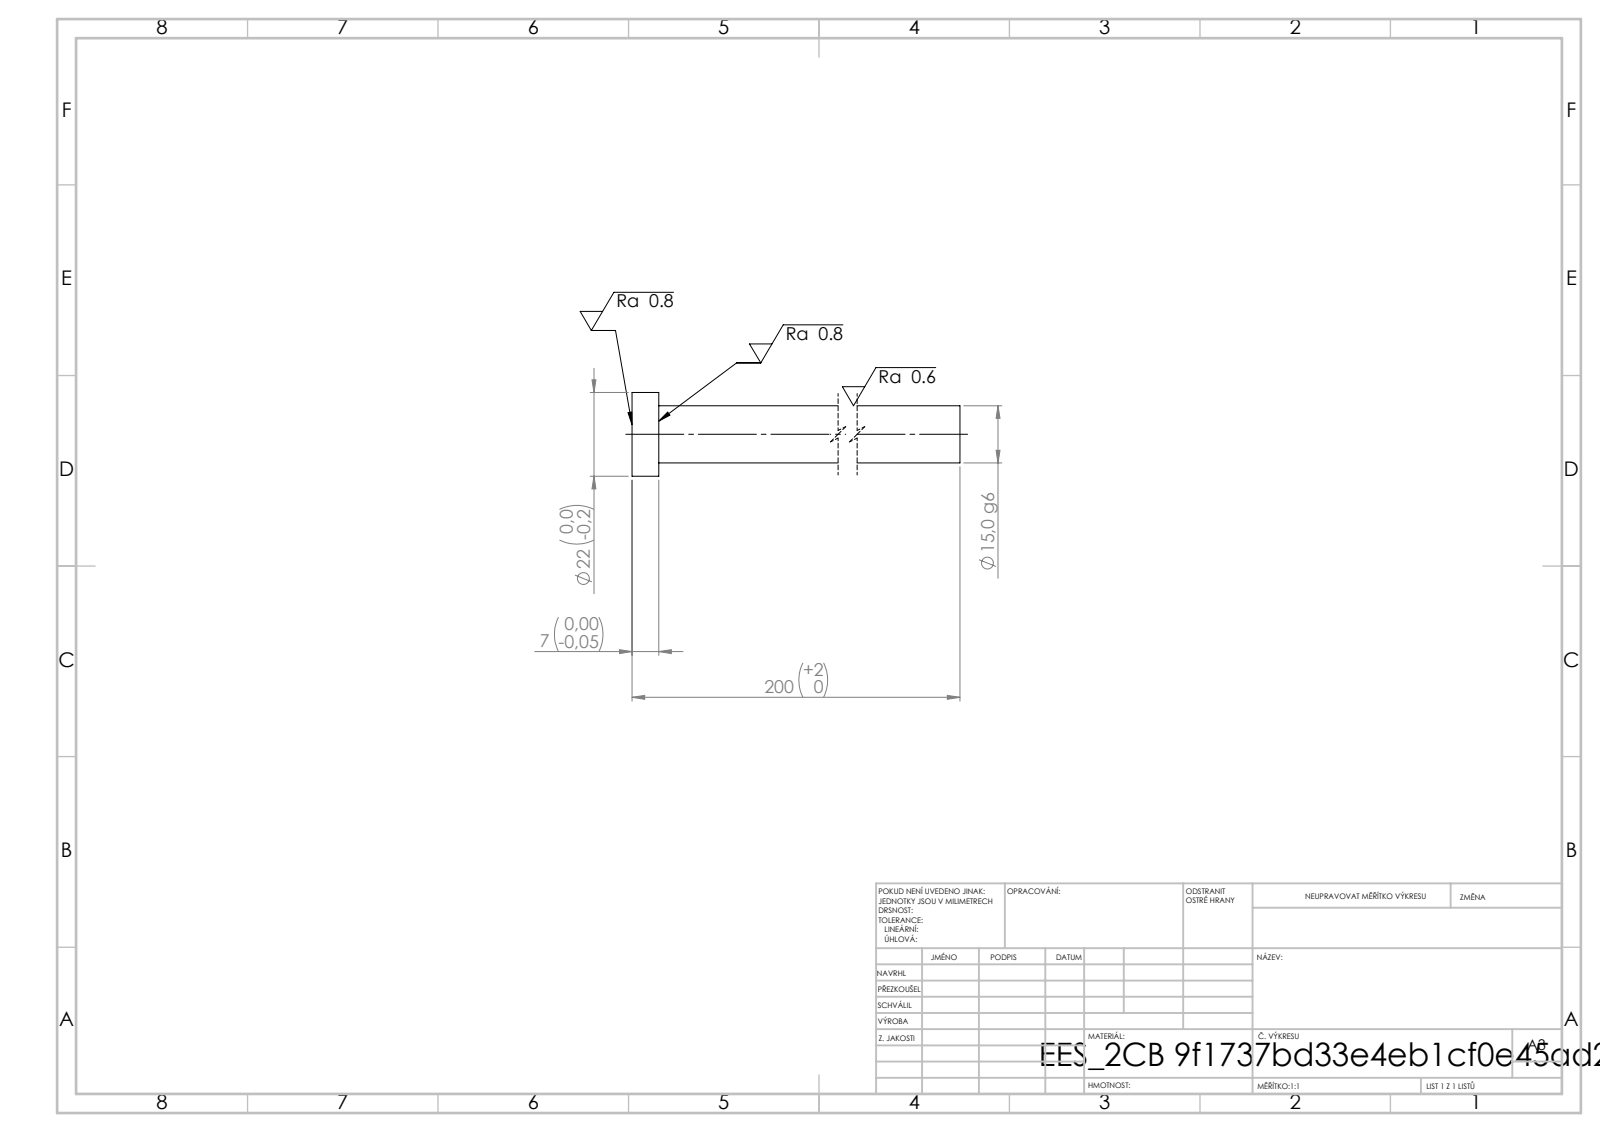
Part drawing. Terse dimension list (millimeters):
written by: SolidWorks 2019 (CONFIG_CONTROL_DESIGN)
unit: mm
bodies: 1 solid, 7 faces (3 planar, 4 cylindrical, 0 other)
size: 200 × 22 × 22
volume: 36 767 mm³; area: 10 339 mm²
bosses: 1× ⌀22, 1× ⌀15
face distances: 7, 200, 193
